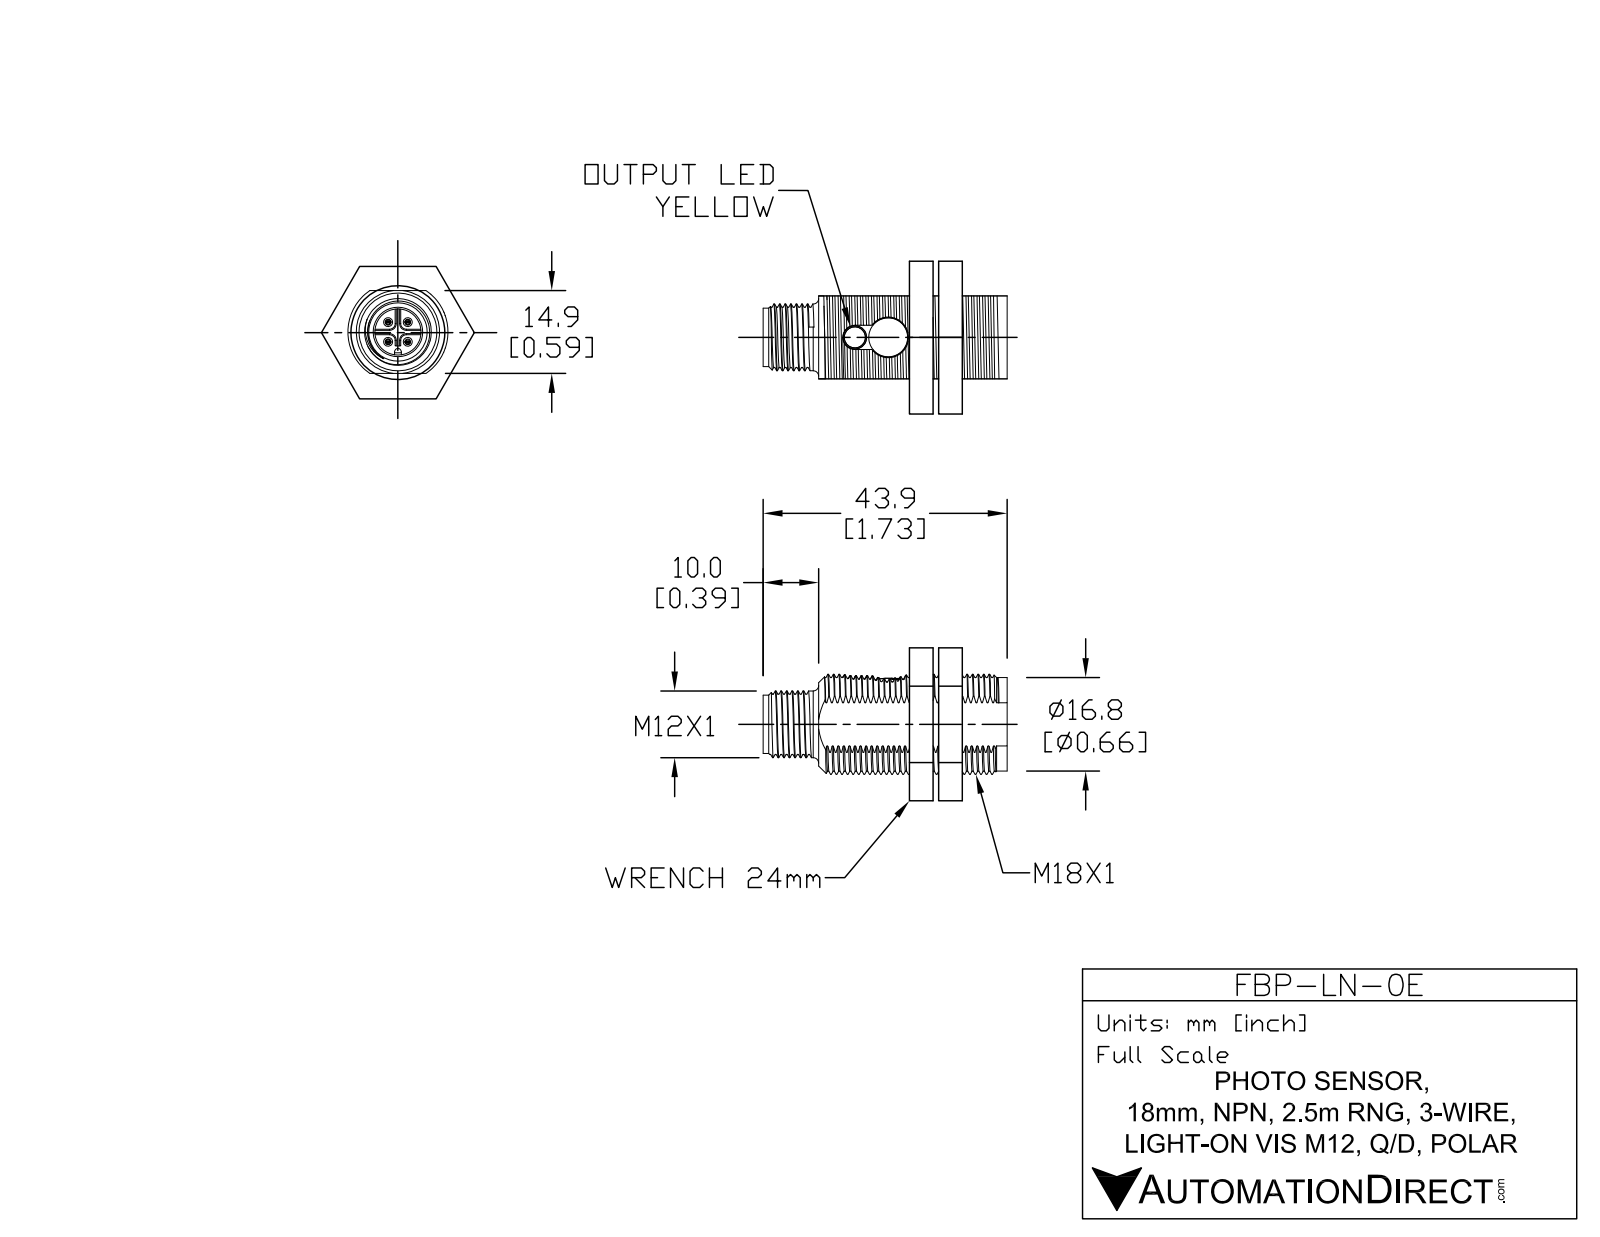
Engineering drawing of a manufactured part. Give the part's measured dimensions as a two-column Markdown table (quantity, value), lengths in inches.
| quantity | value |
| --- | --- |
| part name | FBP-LN-0E |
| STEP written by | SolidWorks 2011 (AUTOMOTIVE_DESIGN) |
| units | inches |
| bodies | 7 solids, 206 faces (128 planar, 30 cylindrical, 48 other) |
| overall size | 1.728 × 1.09 × 0.967 |
| volume | 0.628 in³ |
| surface area | 7.989 in² |
| round holes (diameter × count) | 0.093 × 1, 0.168 × 1, 0.285 × 1, 0.331 × 1 |
| round bosses / shafts (diameter × count) | 0.039 × 4, 0.472 × 1, 0.409 × 1 |
| partial cylindrical surfaces (radius × count) | 0.254 × 2, 0.294 × 2, 0.02 × 1, 0.331 × 1, 0.335 × 1, 0.354 × 1 |
| main face-to-face distances | 0.315, 0.177, 0.945, 0.591, 0.039, 0.492, 0.193, 0.138, 0.508, 0.547 |
| hole center spacings | 0.26 |
